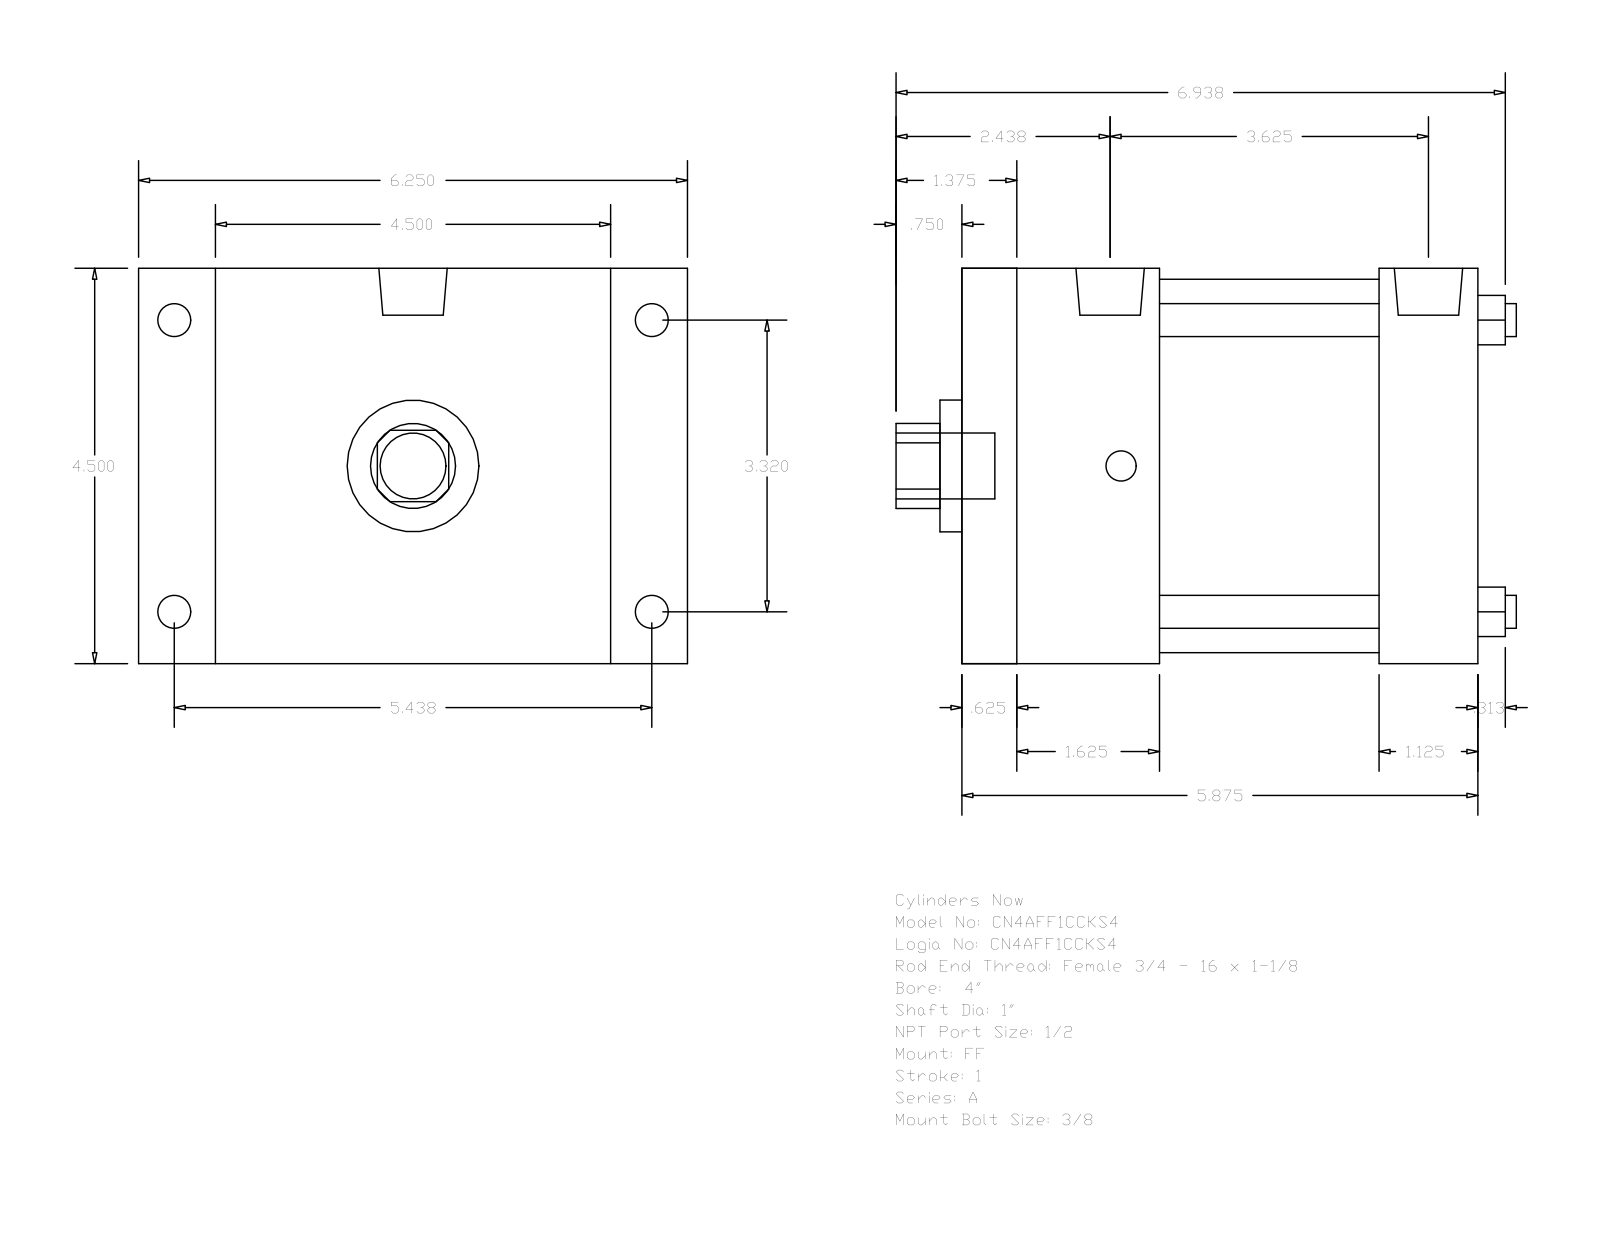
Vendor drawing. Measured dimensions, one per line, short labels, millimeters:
name: A_FF__0400_1
written by: GSSL Pune (CONFIG_CONTROL_DESIGN)
unit: mm
bodies: 0 solids, 92 faces (64 planar, 28 cylindrical, 0 other)
size: 179.39 × 158.75 × 114.3
holes: 4× ⌀9.53, 1× ⌀25.4, 1× ⌀38.1, 1× ⌀107.95
bosses: 4× ⌀9.53, 4× ⌀8.73, 2× ⌀19.77, 1× ⌀19.05
rounds: 1× R12.29
face distances: 114.3, 149.23, 15.87, 133.36, 63.5, 22.23, 136.53, 120.65, 104.78, 28.58
hole spacings: 59.62, 84.32, 119.25
